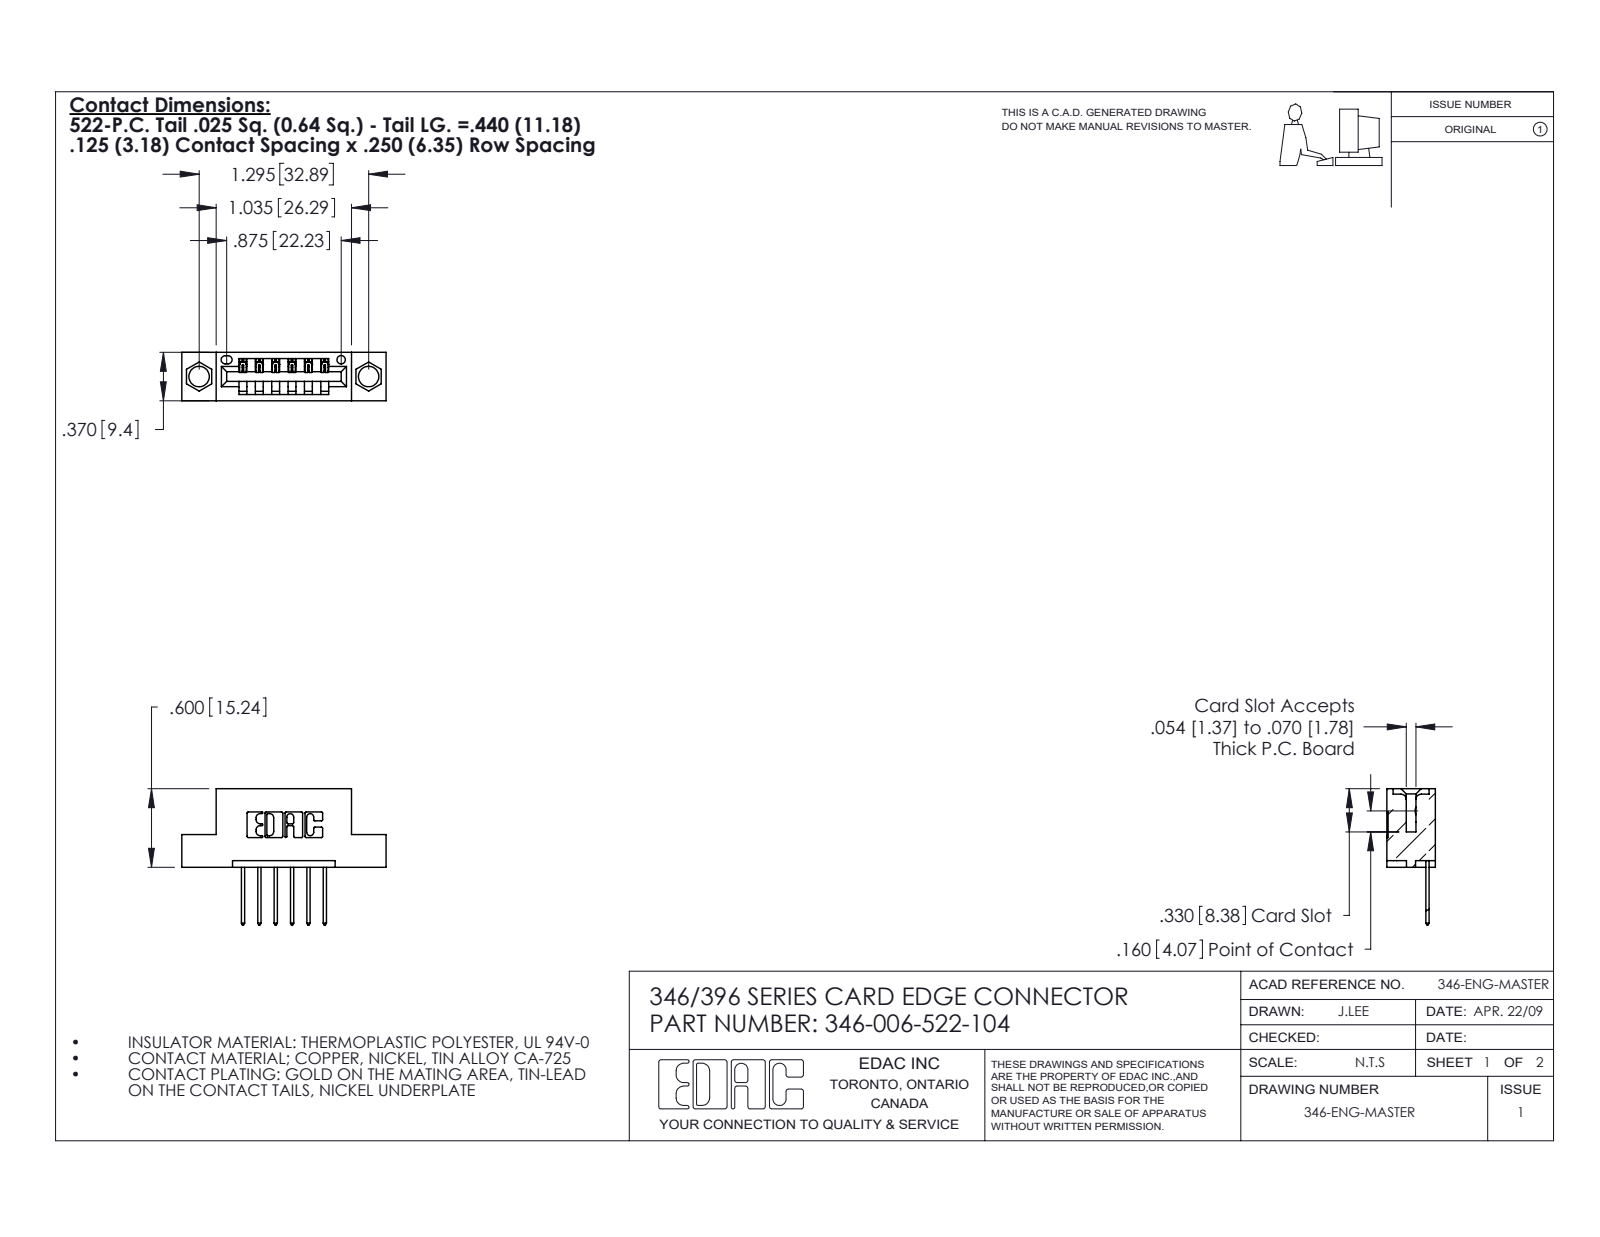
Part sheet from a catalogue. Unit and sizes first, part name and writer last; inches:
Units: inches
Overall size (bounding box): 1.56 × 1.04 × 0.37
Round holes (diameter × count): ⌀0.156 ×2, ⌀0.064 ×1
Partial cylindrical surfaces — rounded edges, fillets, slot ends (radius × count): R0.01 ×22, R0.006 ×12, R0.01 ×12, R0.007 ×6, R0.031 ×6, R0.026 ×3, R0.031 ×2, R0.04 ×2
Main face-to-face distances: 0.25, 0.37, 0.048, 0.322, 0.072, 0.298, 0.025, 0.148, 0.222, 0.1
Hole centre spacings: 0.246, 1.092, 1.295
Volume: 0.21 in³ · Surface area: 5.843 in²
Bodies: 7 solids, 484 faces (330 planar, 154 cylindrical, 0 other)
Part name (STEP PRODUCT): 345-292-001_345-293-122; 346 Part_Flush Mounting Lugs - 0.156 Dia-TH; 346-006-522-104
STEP written by: SolidWorks 2020 (CONFIG_CONTROL_DESIGN)
